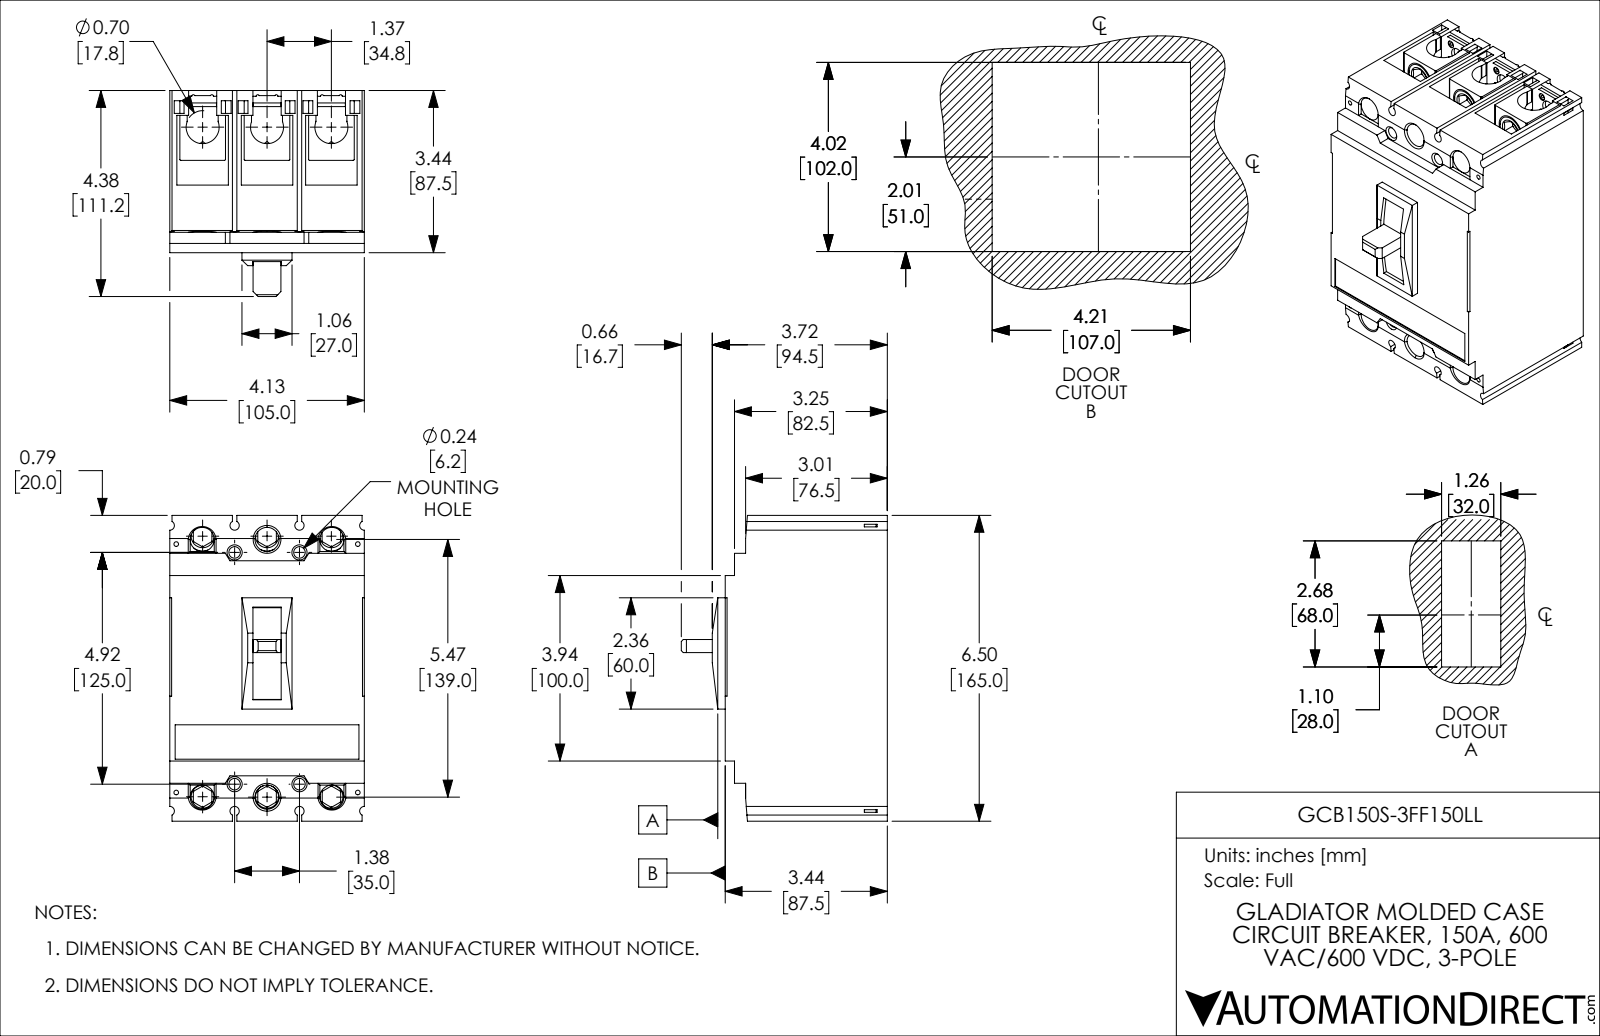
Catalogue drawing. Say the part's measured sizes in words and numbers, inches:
The part is named "GCB150S-3FF150LL". Its 3-D file was written by "SolidWorks 2021 (CONFIG_CONTROL_DESIGN)". It is 19 solids with 1004 faces: 544 planar, 381 cylindrical and 79 other. Overall it measures 6.496 by 4.376 by 4.134 inches. Its volume is 80.08 cubic inches and its surface area 248.1 square inches. Round holes: 24 of diameter 0.067, 24 of diameter 0.157, 10 of diameter 0.098, 6 of diameter 0.354, 6 of diameter 0.512, 6 of diameter 0.689, 4 of diameter 0.197, 4 of diameter 0.244. Round bosses or shafts: 6 of diameter 0.709. Partial cylindrical surfaces (rounded edges, fillets, slot ends): 36 of radius 0.039, 24 of radius 0.008, 6 of radius 0.016, 6 of radius 0.02, 6 of radius 0.031, 4 of radius 0.098, 3 of radius 0.35, 1 of radius 5.638. The main face-to-face distances are 1.368, 4.134, 0.063, 1.031, 0.846, 0.866, 3.445, 5.63, 2.736, 0.264. The hole center spacings are 1.378, 0.285, 1.368, 0.571, 0.742, 0.75, 5.242, 5.809.
